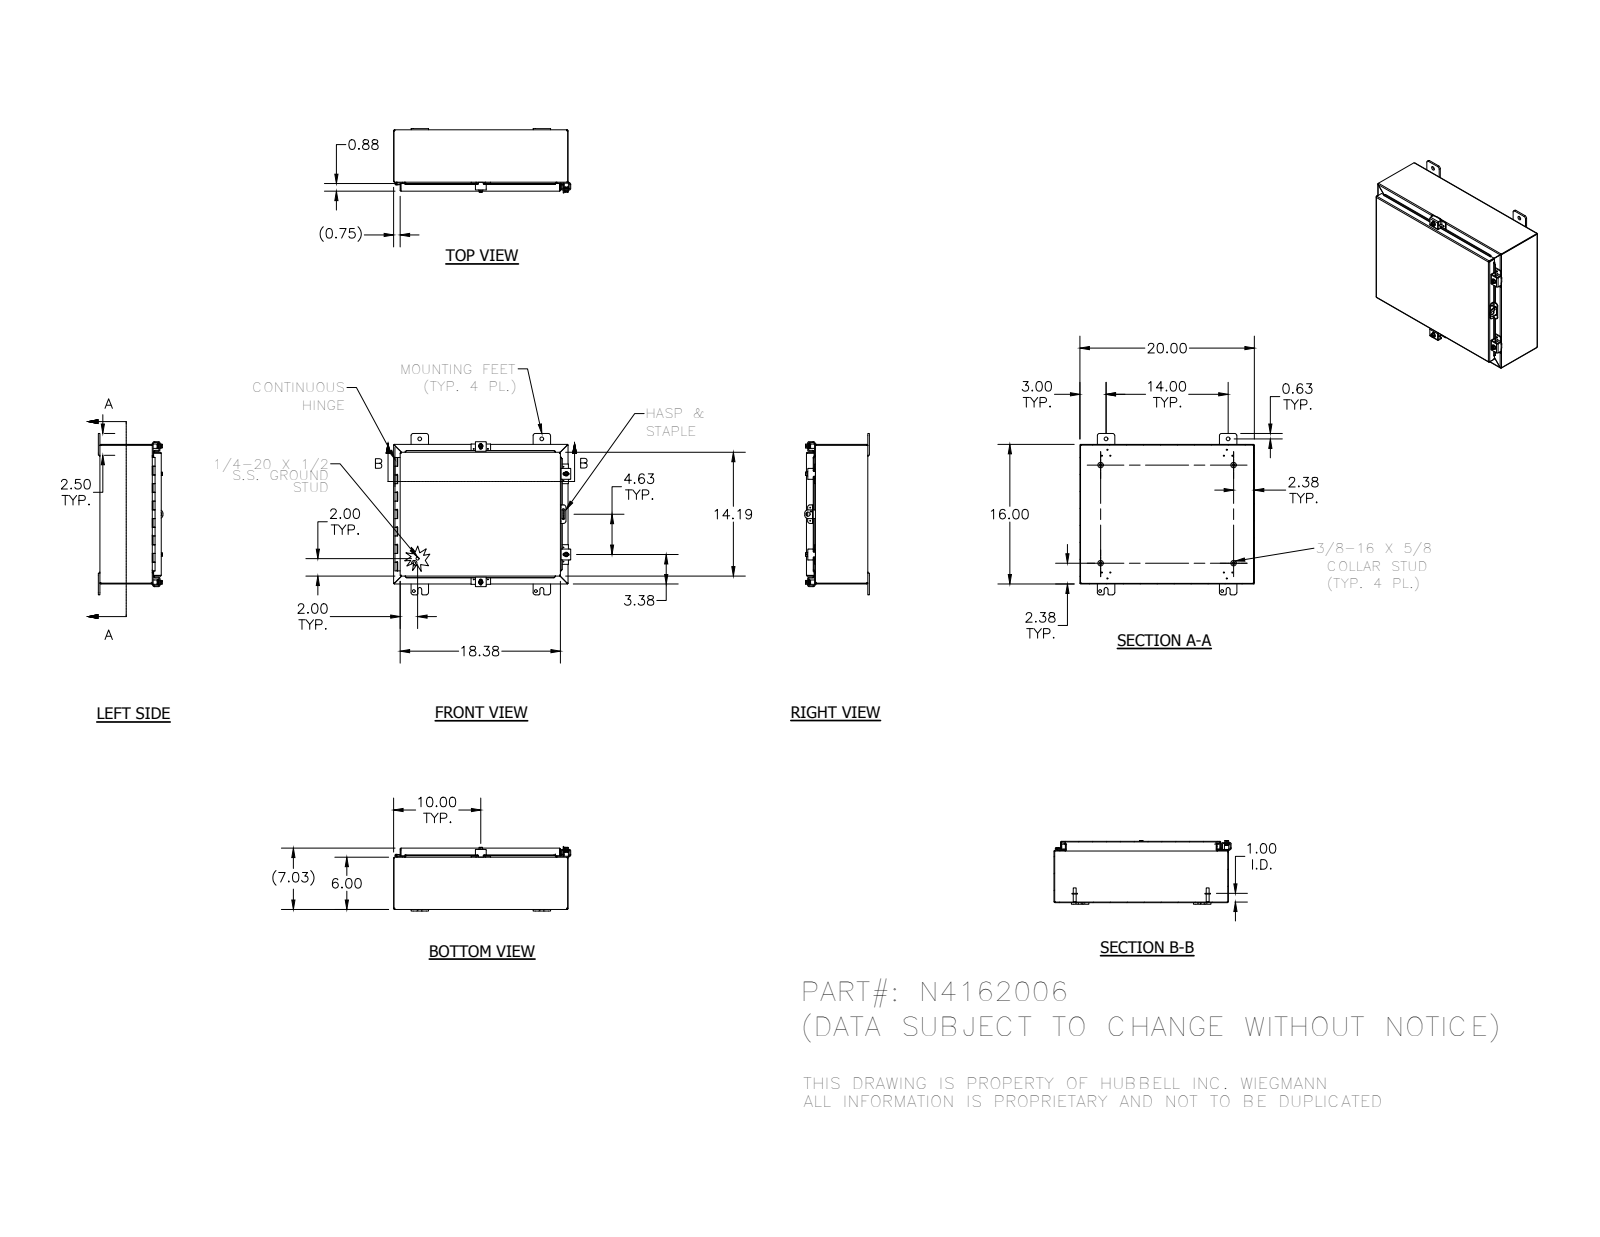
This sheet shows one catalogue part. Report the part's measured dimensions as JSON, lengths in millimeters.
{"part_name": "N4162006BKP_1; HFW30825-4_1; 38420_1; HFW30825-2_1 (+8 more)", "step_written_by": "SolidWorks 2014 (AUTOMOTIVE_DESIGN)", "units": "millimeters", "bodies": {"solids": 37, "faces": 1568, "planar": 611, "cylindrical": 700, "other": 257}, "overall_size": [515.9, 469.9, 188.2], "volume_mm3": 1709000, "surface_area_mm2": 1734000, "round_holes": [[3, 12], [2.8, 11], [5.4, 4], [7.1, 4], [7.6, 4], [8, 4], [11.1, 4], [3.2, 1], [4, 1], [12.7, 1]], "round_bosses_or_shafts": [[6.4, 6], [15.9, 4], [13.2, 4], [12.7, 4], [8.9, 4], [8.4, 4], [2.9, 2], [8.6, 1]], "partial_cylinders_radius": [[0.8, 49], [3.2, 33], [1.6, 29], [6.4, 29], [0.8, 23], [2.7, 23], [1.6, 10], [1.8, 8]], "face_to_face_distances": [1.9, 176.8, 174.9, 178.6, 404.5, 506.1, 150.5, 26.2, 402.6, 406.4], "hole_center_spacings": [355.6, 22.3, 19.3, 21.3, 23.9, 24.6, 40.5, 50.7]}
